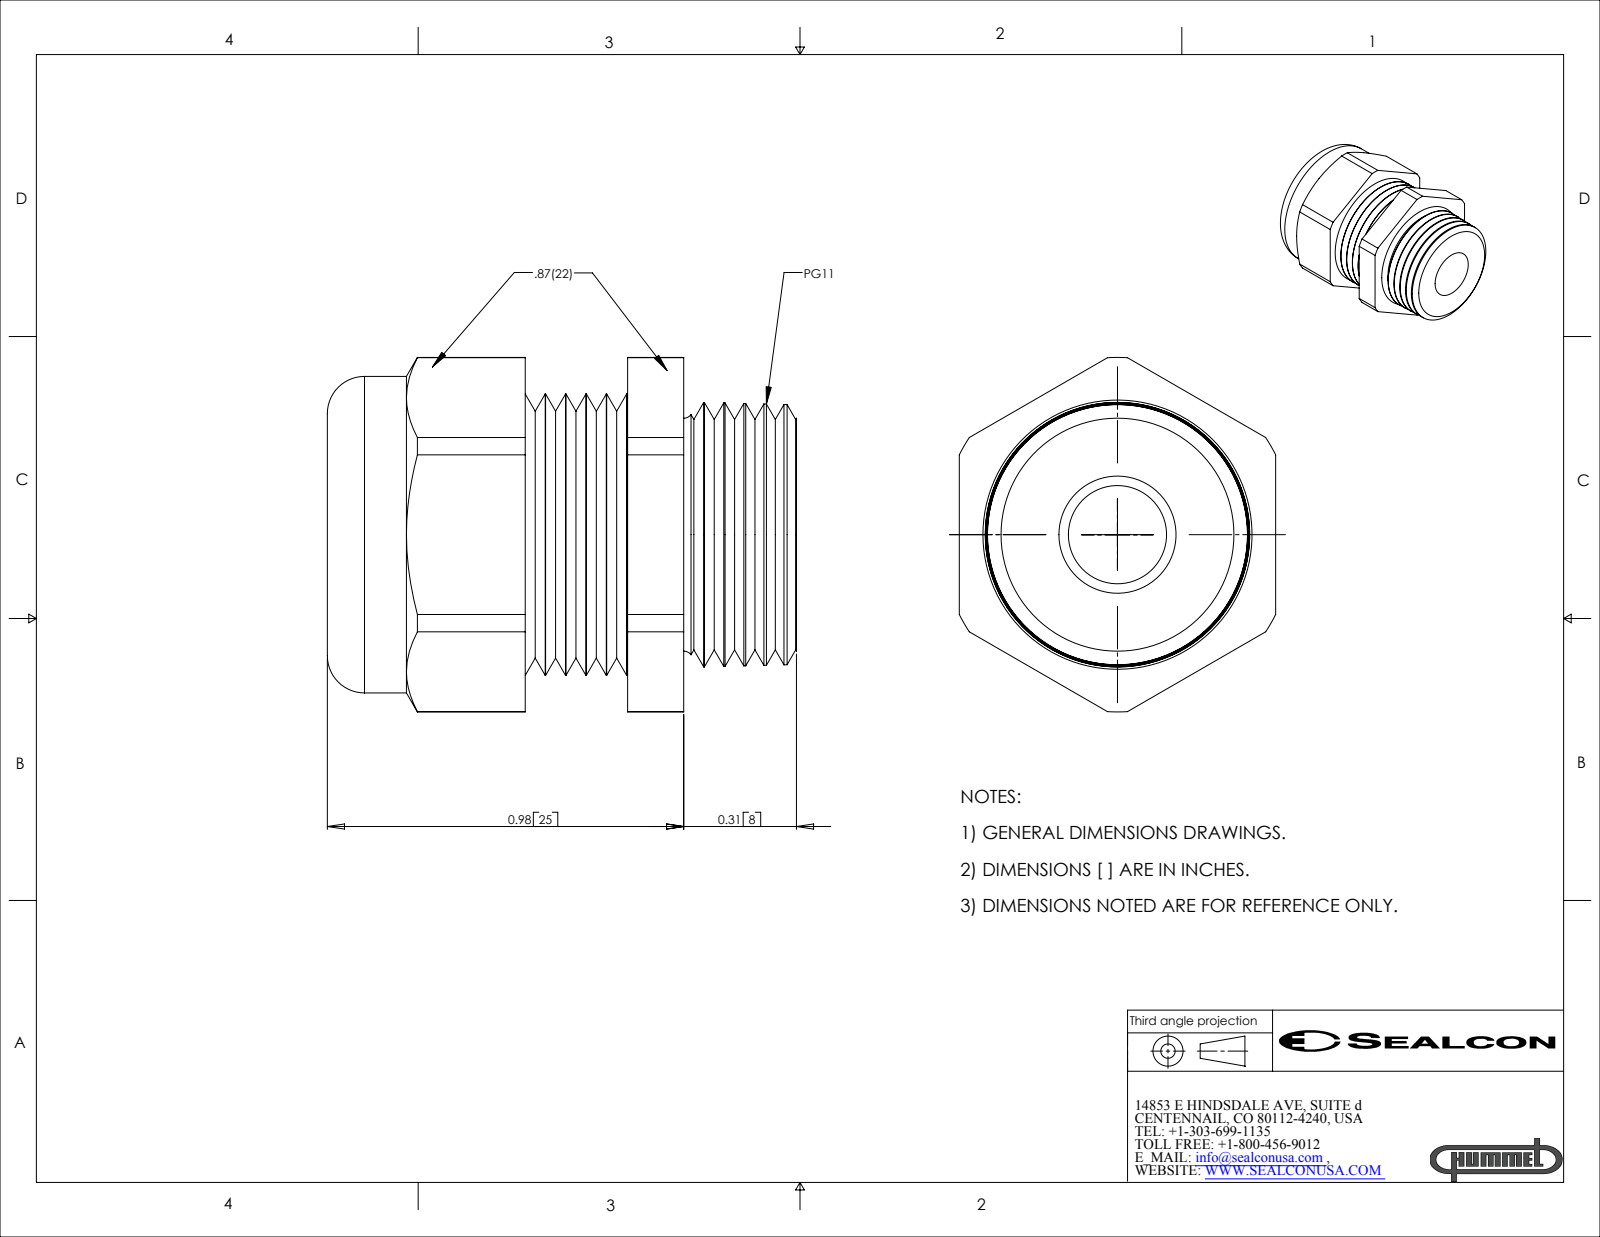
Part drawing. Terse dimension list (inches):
name: CD11AR-BK
written by: SolidWorks 2007 (CONFIG_CONTROL_DESIGN)
unit: in
bodies: 2 solids, 128 faces (20 planar, 34 cylindrical, 74 other)
size: 1.29 × 0.974 × 0.87
volume: 0.573 in³; area: 8.766 in²
holes: 1× ⌀0.27, 1× ⌀0.62
bosses: 1× ⌀0.87, 1× ⌀0.774
rounds: 1× R0.487
face distances: 0.87, 1.072, 0.197, 1.27, 0.96, 0.763, 0.31, 0.524, 0.327, 0.436
